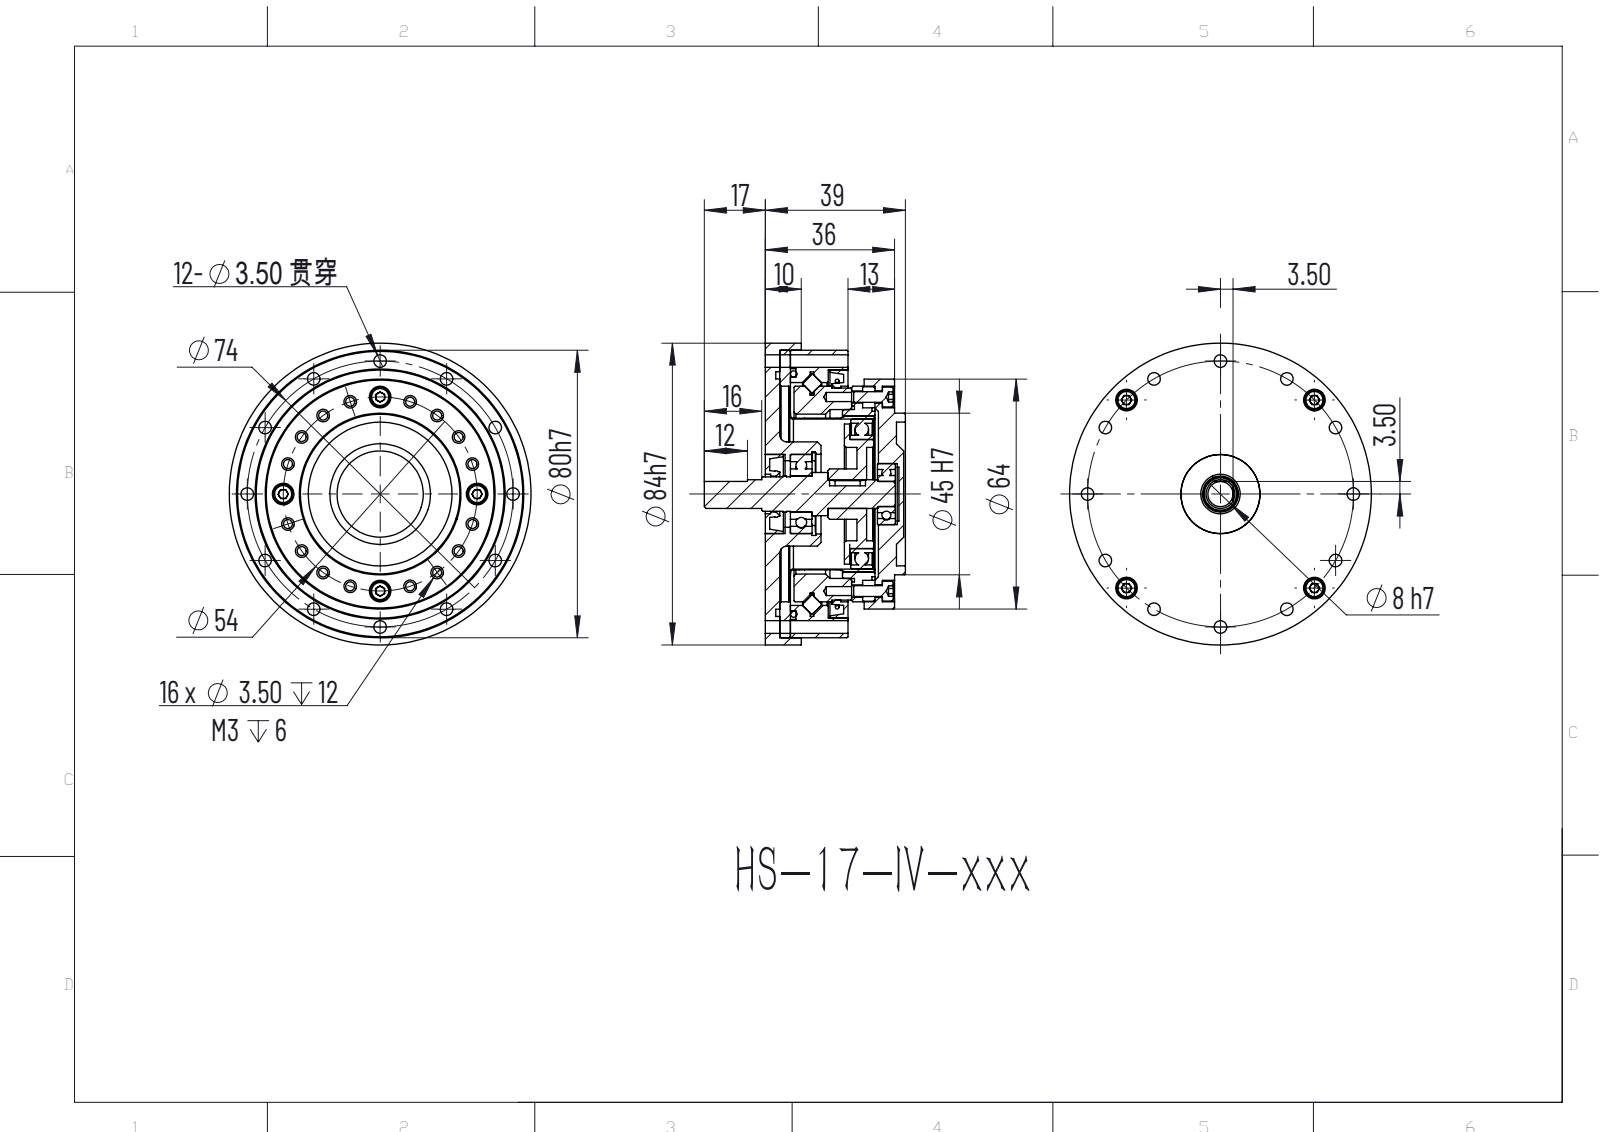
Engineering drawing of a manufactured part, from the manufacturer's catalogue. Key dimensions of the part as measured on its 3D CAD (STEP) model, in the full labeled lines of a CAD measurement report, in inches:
Part name (STEP PRODUCT): HS-17-IV; hexagon socket head cap screws gb_GB_FASTENER_SCREWS_HSHCS M3X8-C; deep groove ball bearings gb_Rolling bearings 61900 GB 276-94; 3??????? (+8 more)
STEP written by: ONSHAPE BY PTC INC, 1.201 (AP242_MANAGED_MODEL_BASED_3D_ENGINEERING_MIM_LF)
Units: inches
Bodies: 98 solids, 1259 faces (620 planar, 345 cylindrical, 294 other)
Overall size (bounding box): 3.307 × 3.307 × 2.205
Volume: 7.258 in³ · Surface area: 157.5 in²
Round holes (diameter × count): ⌀0.138 ×36, ⌀0.098 ×26, ⌀0.134 ×8, ⌀0.236 ×8, ⌀0.079 ×2, ⌀0.063 ×1, ⌀0.094 ×1, ⌀0.169 ×1, ⌀0.276 ×1, ⌀0.394 ×1, ⌀0.433 ×1, ⌀0.538 ×1
Round bosses / shafts (diameter × count): ⌀0.157 ×36, ⌀0.217 ×8, ⌀0.118 ×8, ⌀3.307 ×1, ⌀3.15 ×1, ⌀2.559 ×1, ⌀2.524 ×1, ⌀2.52 ×1
Partial cylindrical surfaces — rounded edges, fillets, slot ends (radius × count): R0.08 ×36, R0.047 ×2, R0.059 ×2, R0.079 ×2, R0.388 ×1
Main face-to-face distances: 0.157, 0.039, 0.276, 0.118, 0.295, 0.925, 0.63, 0.512, 0.591, 0.335
Hole centre spacings: 1.063, 1.503, 1.894, 0.657, 0.965, 1.457, 2.022, 0.332
